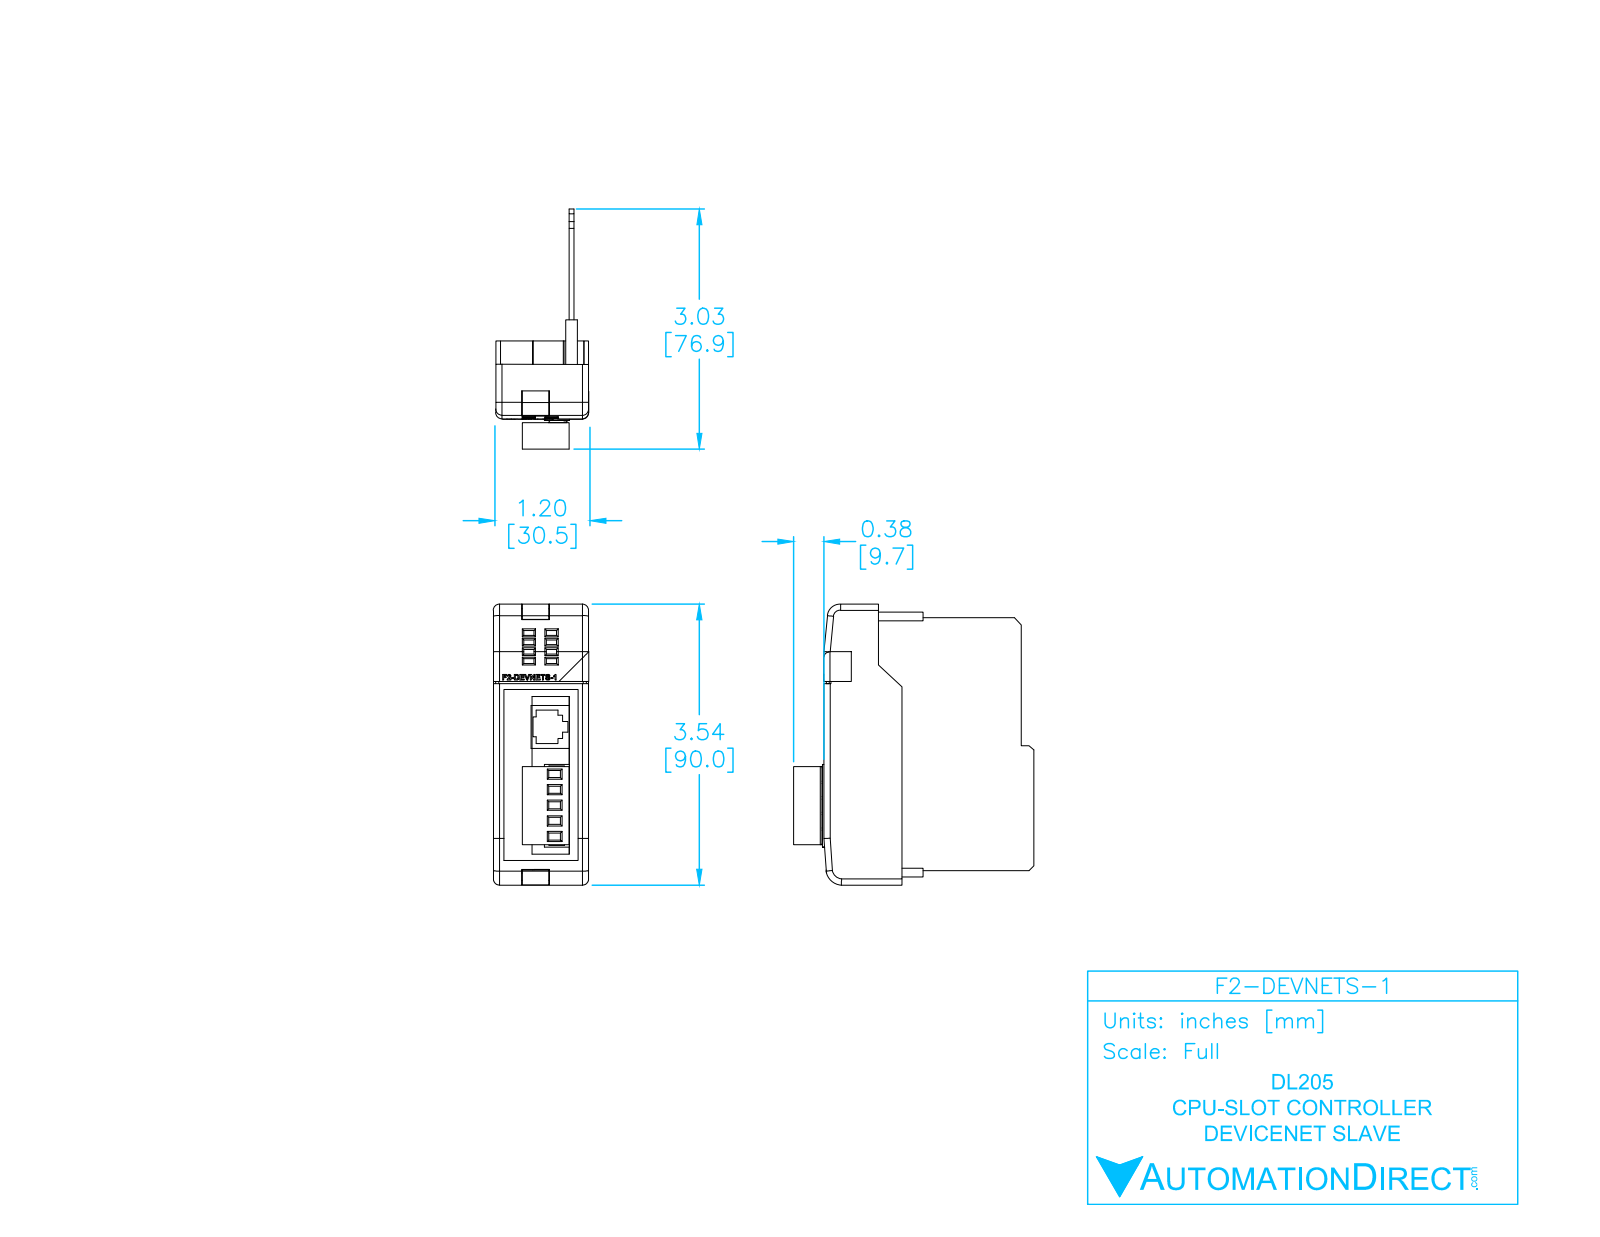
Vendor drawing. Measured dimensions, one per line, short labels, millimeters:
name: F2-DEVNETS-1
written by: SolidWorks 2009 (AUTOMOTIVE_DESIGN)
unit: mm
bodies: 10 solids, 633 faces (469 planar, 119 cylindrical, 45 other)
size: 90 × 76.94 × 30.55
volume: 23 336 mm³; area: 32 601 mm²
holes: 5× ⌀4
rounds: 28× R0.5, 11× R2, 5× R2.76, 5× R3.01, 4× R0.25, 2× R1, 1× R2.62, 1× R3.79
face distances: 1.5, 4.72, 3.22, 6.22, 24.28, 29, 0.5, 8.5, 25.78, 30.5
hole spacings: 5, 10, 15, 20
